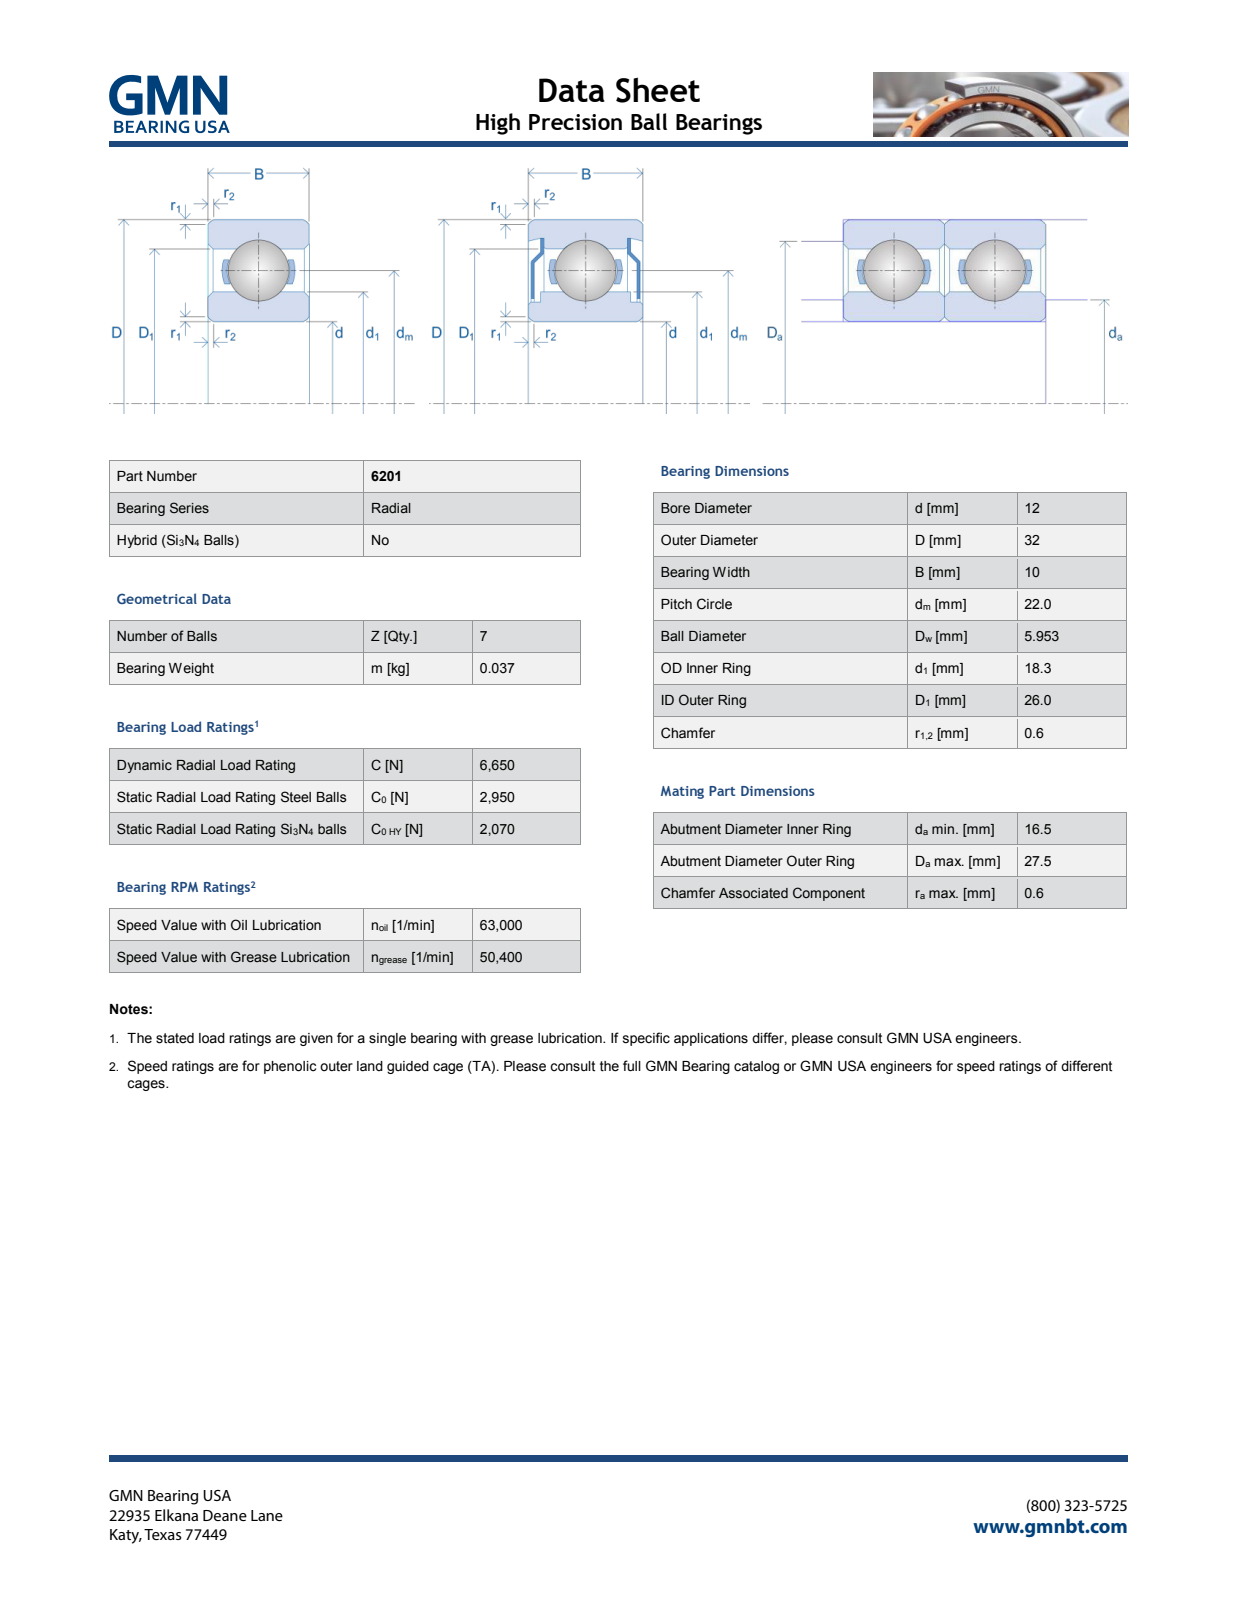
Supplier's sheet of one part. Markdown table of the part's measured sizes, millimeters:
| quantity | value |
| --- | --- |
| part name | 6201_PRT |
| STEP written by | PRO/ENGINEER BY PARAMETRIC TECHNOLOGY CORPORATION, 2013150 (AUTOMOTIVE_DESIGN) |
| units | millimeters |
| bodies | 10 solids, 489 faces (425 planar, 30 cylindrical, 34 other) |
| overall size | 32 × 32 × 10.01 |
| volume | 5 397 mm³ |
| surface area | 5 845 mm² |
| round holes (diameter × count) | 6.15 × 7, 12 × 1, 21.6 × 1, 26 × 1 |
| round bosses / shafts (diameter × count) | 32 × 1, 25.2 × 1, 18.3 × 1 |
| main face-to-face distances | 9.9, 10, 9.8, 9.91, 10.01, 1.4, 1.23, 1.22, 1.05, 0.99 |
